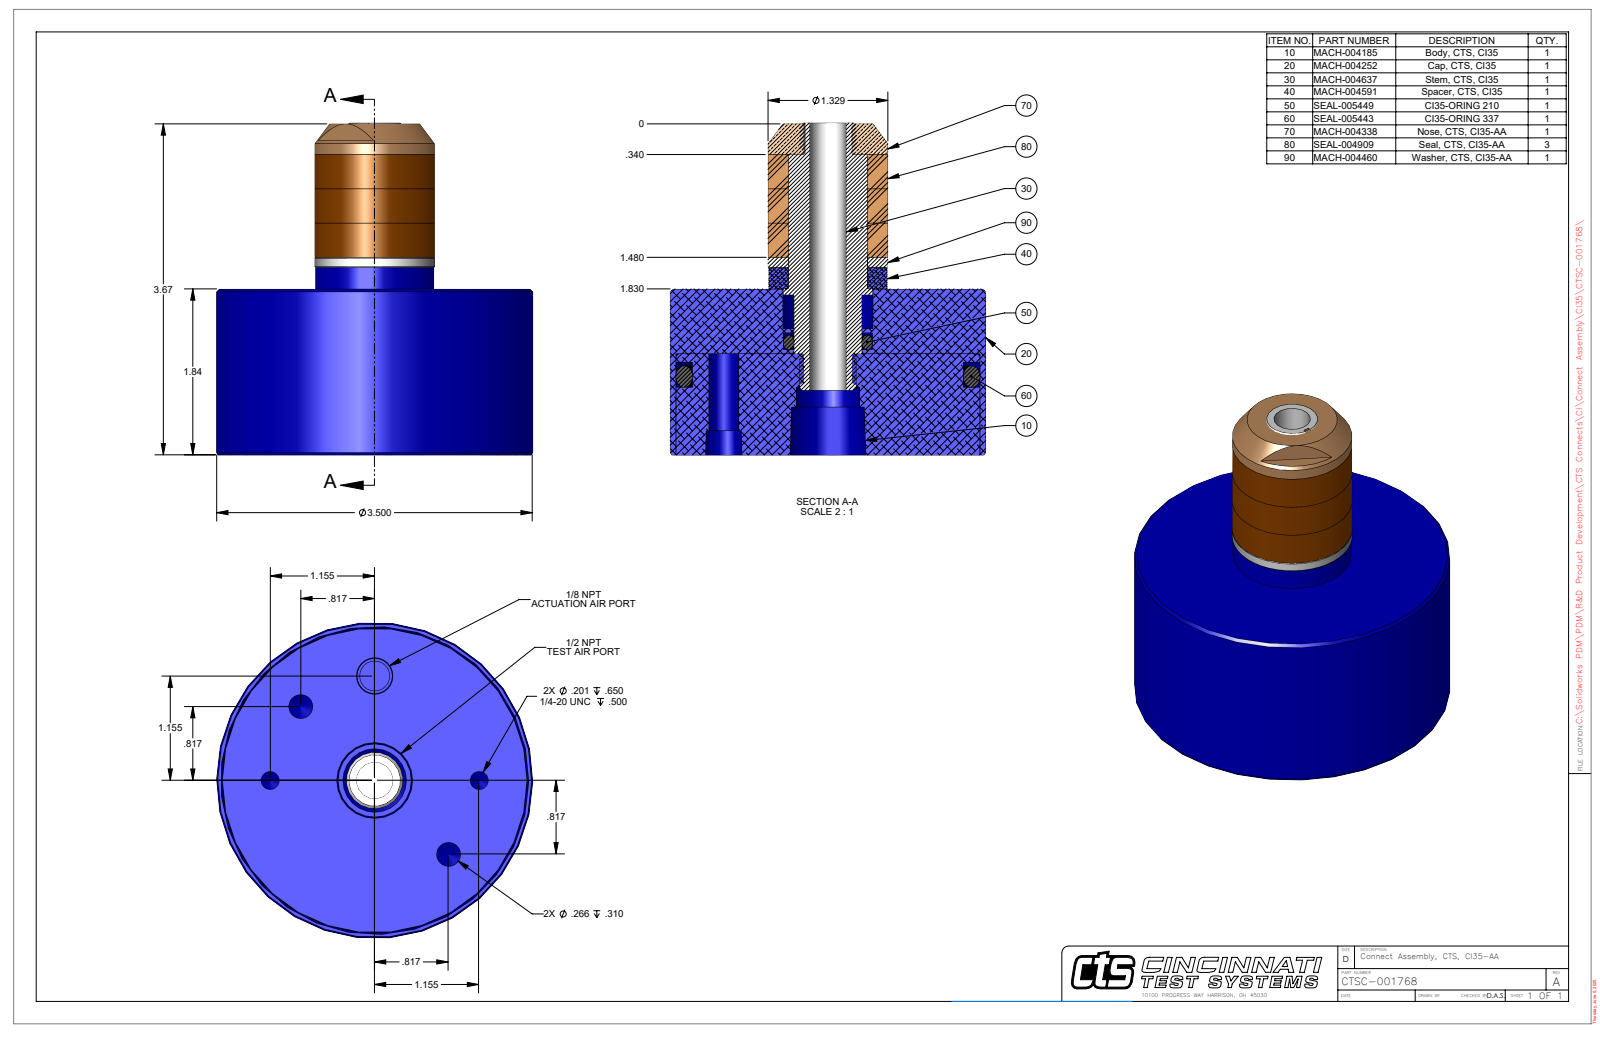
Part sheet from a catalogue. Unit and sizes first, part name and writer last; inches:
Units: inches
Overall size (bounding box): 3.68 × 3.5 × 3.5
Round holes (diameter × count): ⌀0.201 ×2, ⌀0.266 ×2, ⌀0.332 ×1, ⌀0.406 ×1, ⌀0.703 ×1, ⌀3.373 ×1
Round bosses / shafts (diameter × count): ⌀3.5 ×1, ⌀3.365 ×1, ⌀1.329 ×1, ⌀1.312 ×1
Partial cylindrical surfaces — rounded edges, fillets, slot ends (radius × count): R0.266 ×1
Main face-to-face distances: 1.84, 3.67, 1.83, 0.719, 1.121, 2.951, 3.486, 2.767, 1.646, 0.184
Hole centre spacings: 0.884, 1.155, 2.134, 1.155, 1.633, 2.309, 2.31
Volume: 19.22 in³ · Surface area: 69 in²
Bodies: 1 solid, 74 faces (20 planar, 27 cylindrical, 27 other)
Part name (STEP PRODUCT): CTSC-001768
STEP written by: SolidWorks 2023 (AUTOMOTIVE_DESIGN)
